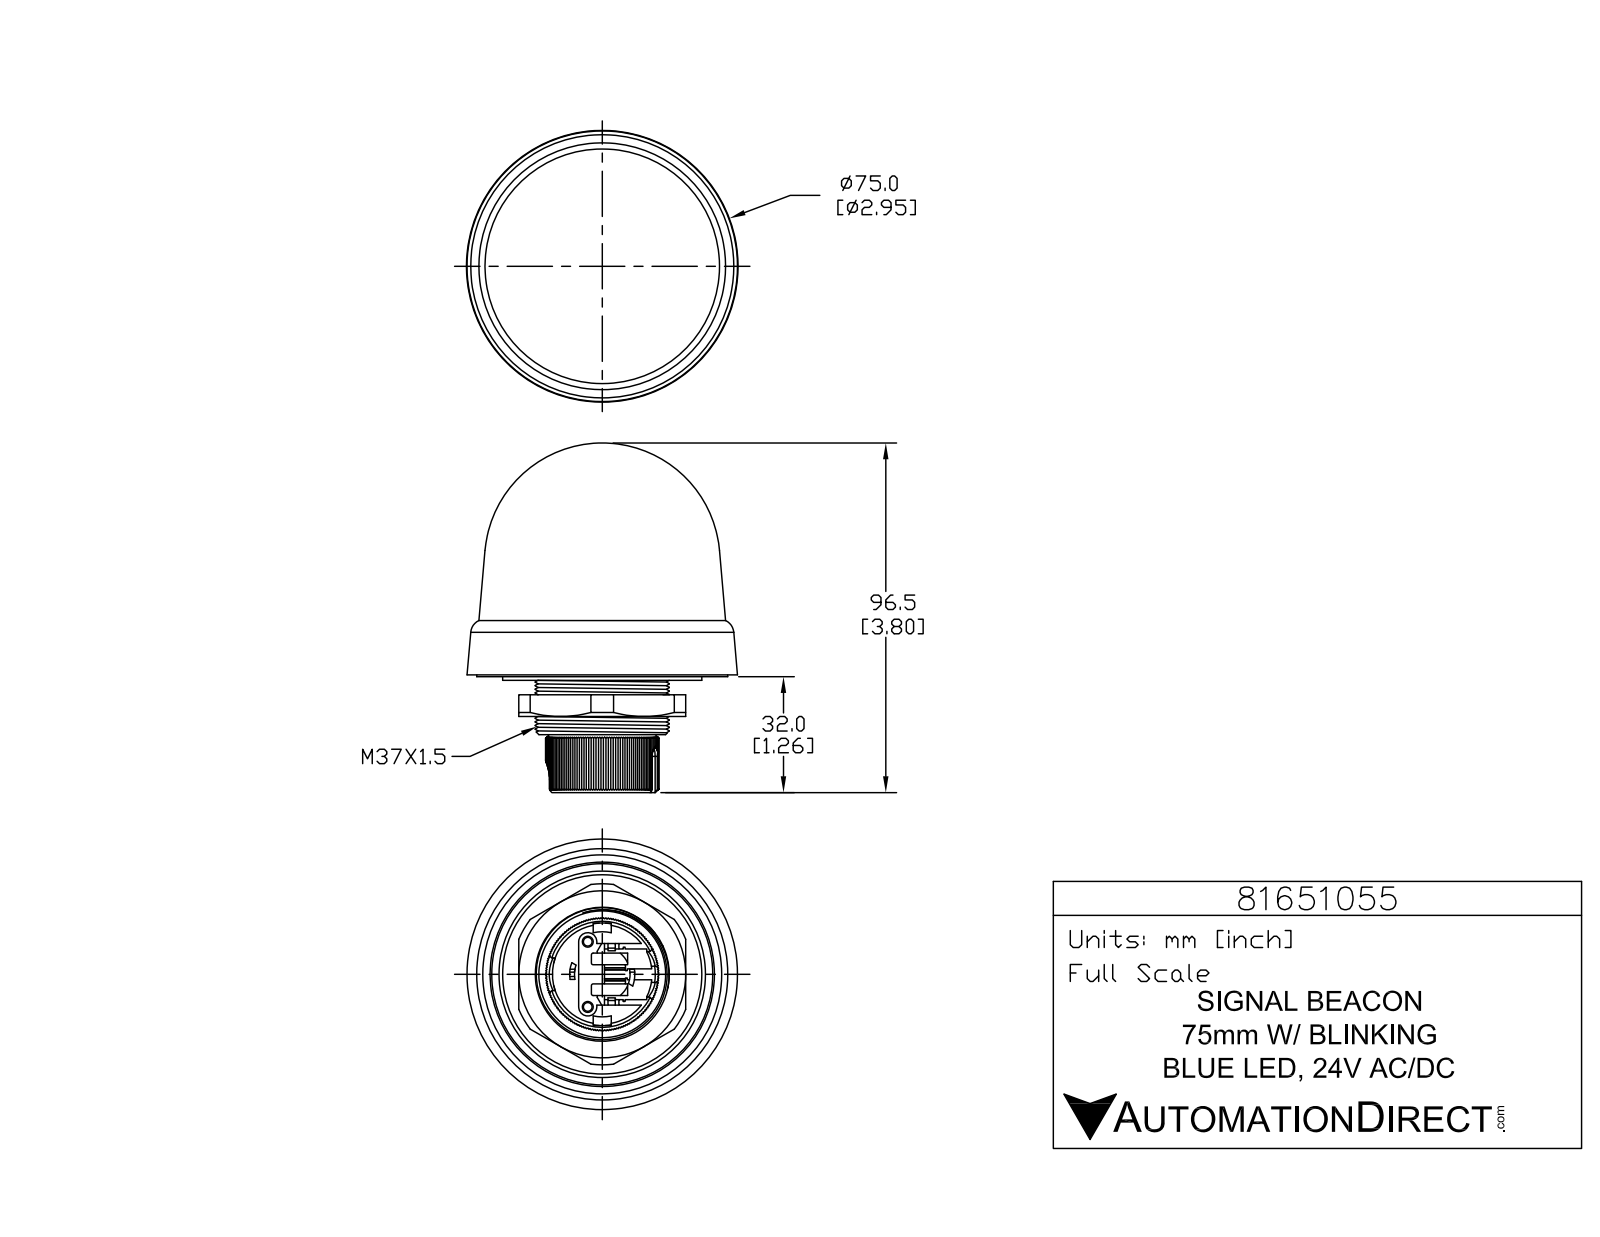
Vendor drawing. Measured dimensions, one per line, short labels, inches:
name: 81651055
written by: SolidWorks 2019 (CONFIG_CONTROL_DESIGN)
unit: in
bodies: 3 solids, 560 faces (432 planar, 80 cylindrical, 48 other)
size: 3.799 × 2.941 × 2.941
volume: 12.36 in³; area: 58.68 in²
holes: 2× ⌀0.094, 2× ⌀0.118, 1× ⌀0.604, 1× ⌀1.142
bosses: 2× ⌀0.217, 2× ⌀0.067, 1× ⌀2.165, 1× ⌀1.457, 1× ⌀0.925
rounds: 6× R0.008, 6× R0.039, 4× R0.02, 2× R0.031, 2× R0.079, 2× R0.098, 1× R0.177, 1× R0.354
face distances: 0.177, 0.354, 0.197, 0.433, 0.512, 0.335, 0.059, 0.394, 0.118, 0.157
hole spacings: 0.388, 0.709
